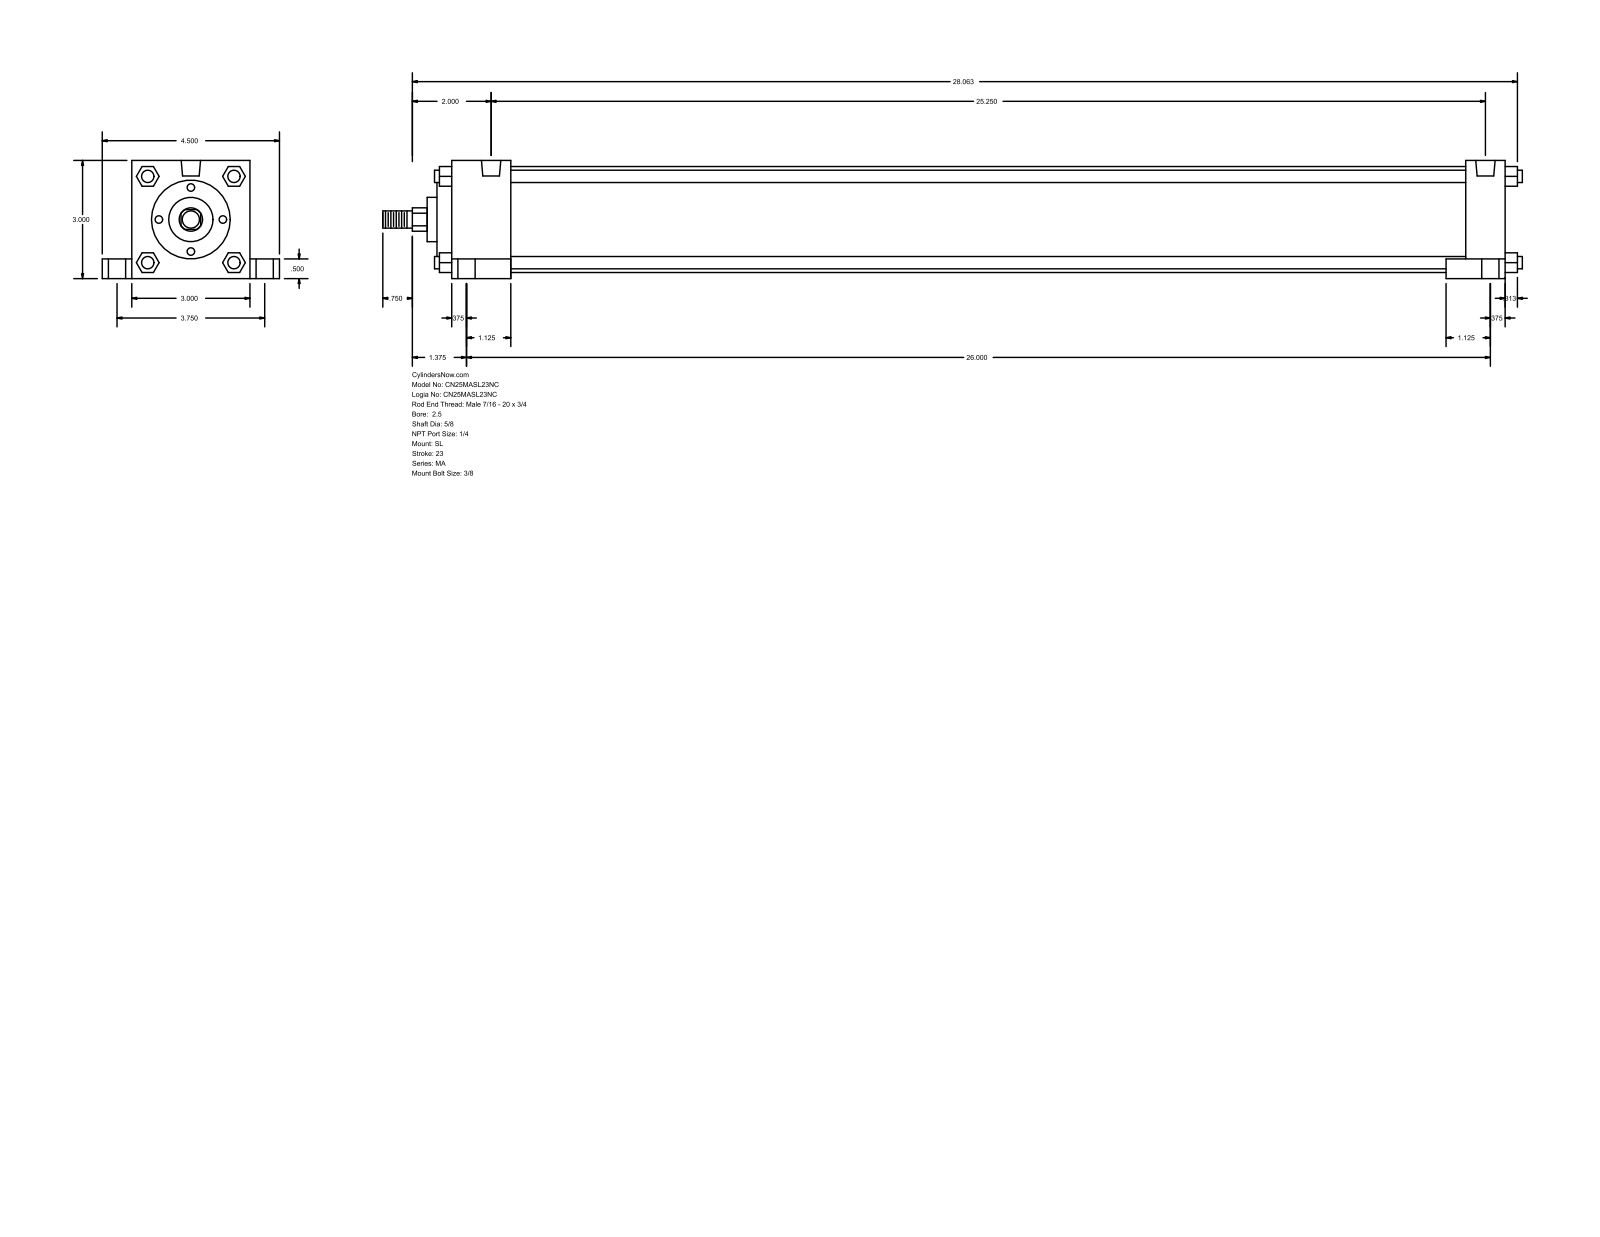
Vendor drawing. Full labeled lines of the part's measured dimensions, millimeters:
Part name (STEP PRODUCT): MA_SL__0250_0.625
STEP written by: GSSL Pune (CONFIG_CONTROL_DESIGN)
Units: millimetres
Bodies: 0 solids, 150 faces (113 planar, 37 cylindrical, 0 other)
Overall size (bounding box): 735.01 × 114.3 × 76.2
Round holes (diameter × count): ⌀7.94 ×4, ⌀11.11 ×4, ⌀17.46 ×4, ⌀12.49 ×2
Round bosses / shafts (diameter × count): ⌀7.94 ×4, ⌀68.33 ×1, ⌀50.8 ×1, ⌀28.57 ×1, ⌀15.88 ×1, ⌀11.11 ×1
Partial cylindrical surfaces — rounded edges, fillets, slot ends (radius × count): R7.54 ×1
Main face-to-face distances: 76.2, 679.45, 12.7, 615.95, 25.4, 38.1, 641.35, 654.05, 19.05, 63.5
Hole centre spacings: 47.73, 50.2, 95.24, 641.35, 646.29, 658.95, 660.41, 667.24
